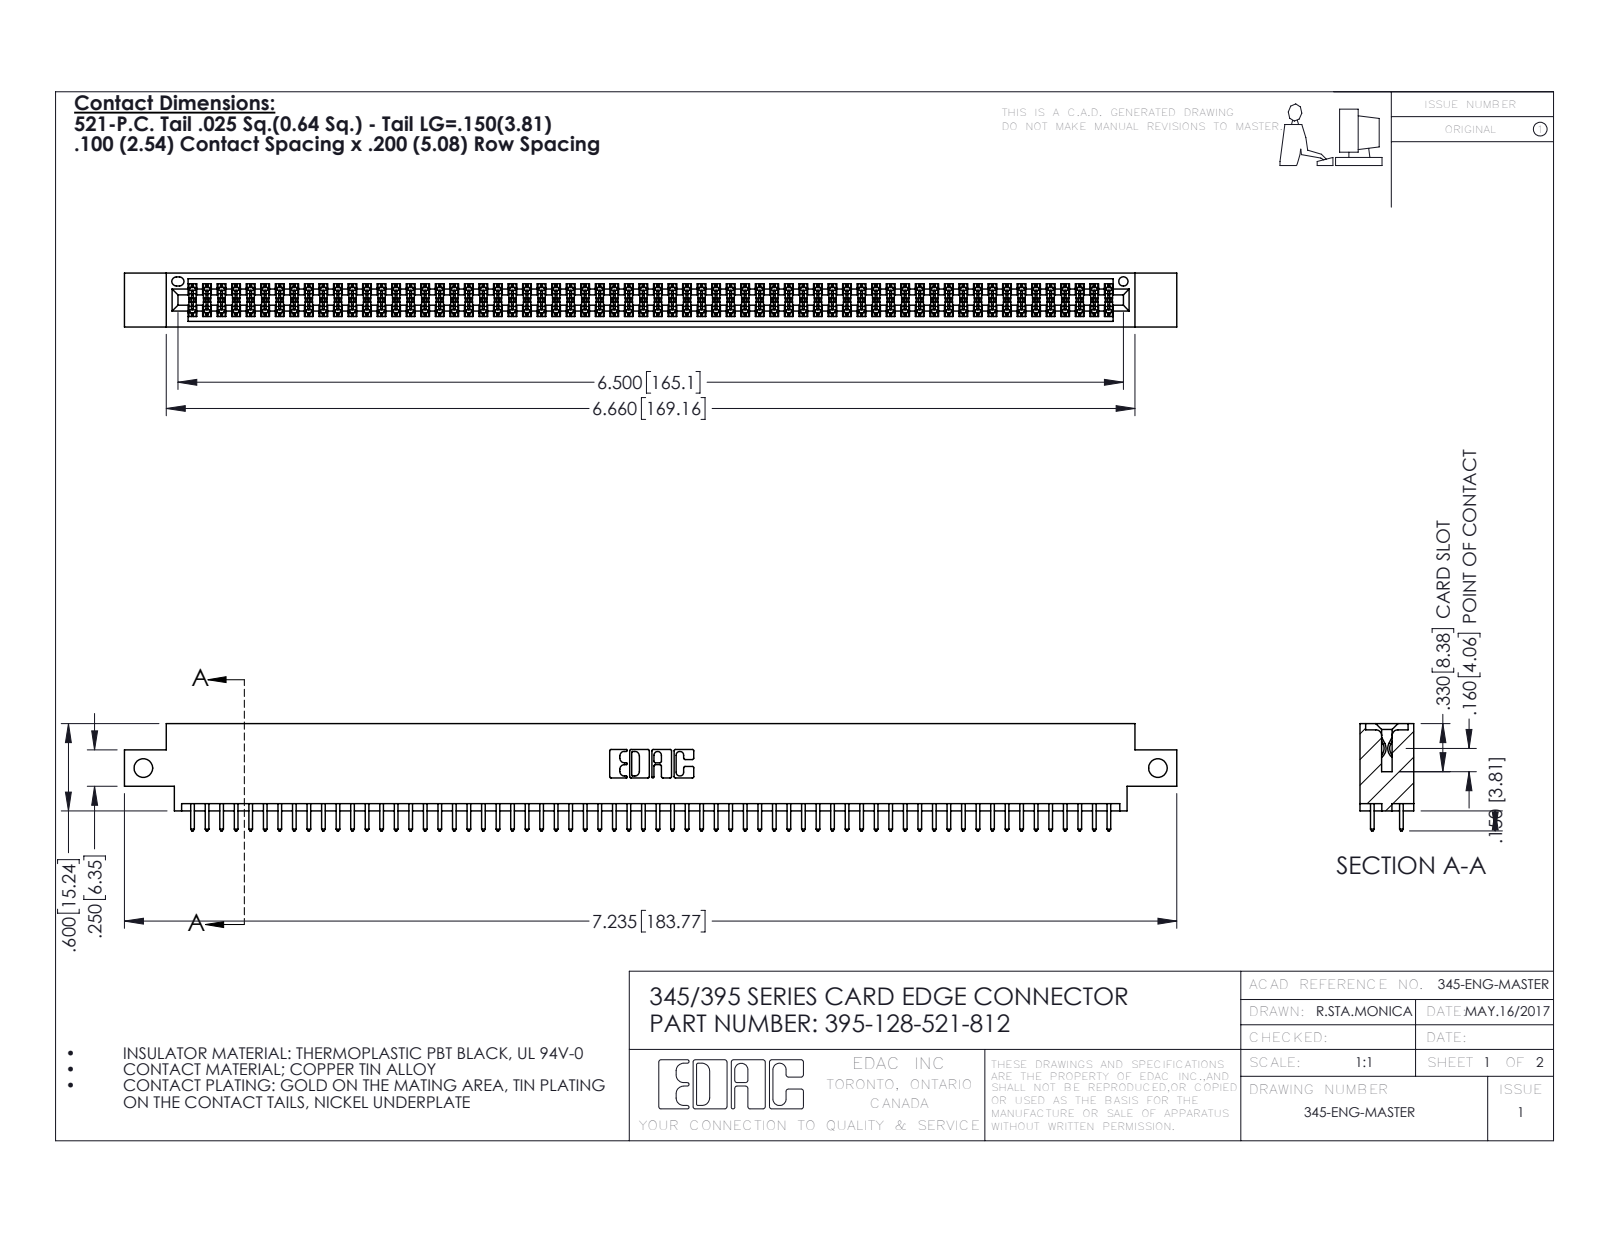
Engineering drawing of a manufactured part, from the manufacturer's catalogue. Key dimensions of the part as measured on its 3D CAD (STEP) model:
Part name (STEP PRODUCT): 345 Part_0.170 Offset - Side Mount; 345-292-001_345-293-121; 395-128-521-812
STEP written by: SolidWorks 2016 (CONFIG_CONTROL_DESIGN)
Units: inches
Bodies: 129 solids, 6530 faces (4308 planar, 2222 cylindrical, 0 other)
Overall size (bounding box): 7.235 × 0.737 × 0.37
Volume: 1.086 in³ · Surface area: 40.93 in²
Round holes (diameter × count): ⌀0.128 ×2, ⌀0.064 ×1
Partial cylindrical surfaces — rounded edges, fillets, slot ends (radius × count): R0.006 ×192, R0.01 ×128, R0.01 ×22, R0.007 ×6, R0.031 ×6, R0.026 ×3, R0.014 ×2, R0.019 ×2
Main face-to-face distances: 0.298, 0.072, 0.2, 0.37, 0.098, 0.272, 0.025, 0.225, 0.175, 0.149
Hole centre spacings: 6.975
